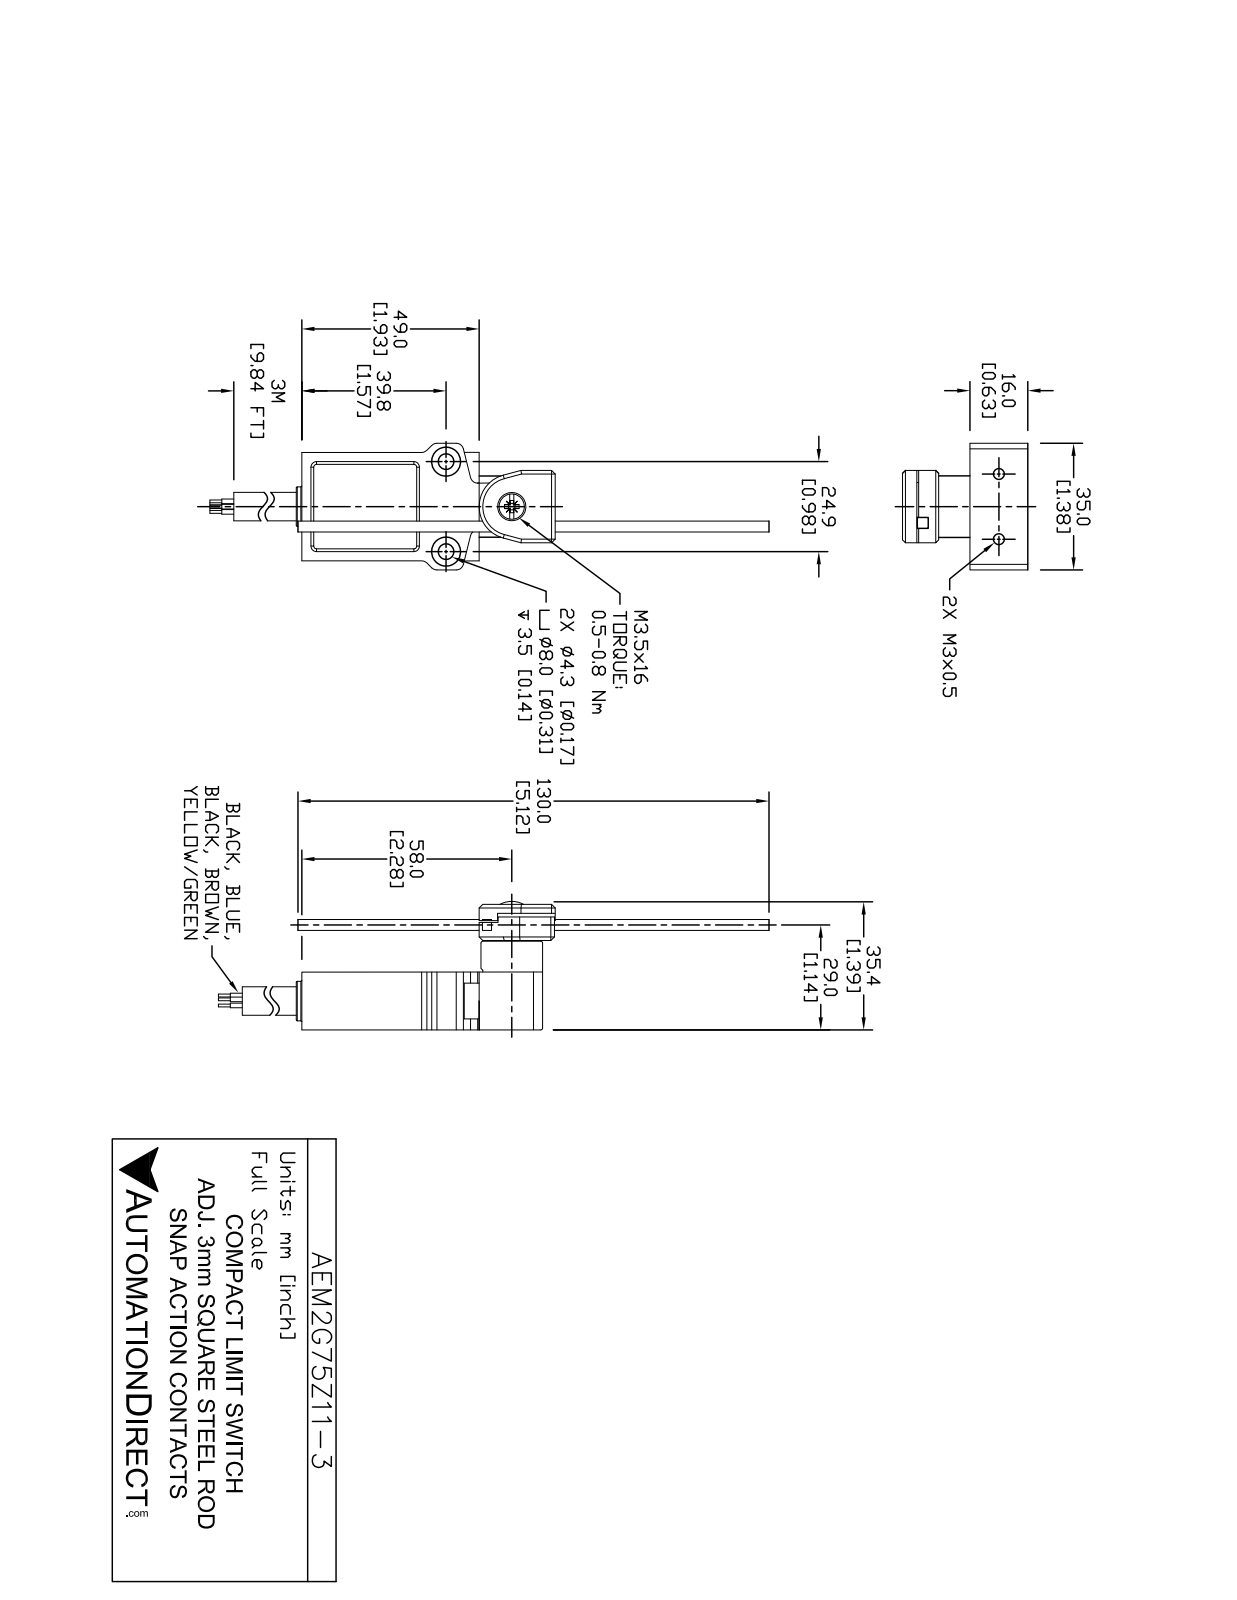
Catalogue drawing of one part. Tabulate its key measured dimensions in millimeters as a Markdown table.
| quantity | value |
| --- | --- |
| part name | AEM2G75Z11-3 |
| STEP written by | SolidWorks 2017 (AUTOMOTIVE_DESIGN) |
| units | millimeters |
| bodies | 7 solids, 223 faces (145 planar, 63 cylindrical, 15 other) |
| overall size | 174.1 × 47.5 × 34.7 |
| volume | 32 200 mm³ |
| surface area | 13 680 mm² |
| round holes (diameter × count) | 3 × 2, 4.4 × 2, 8.2 × 2, 3.5 × 1, 5 × 1, 8 × 1 |
| round bosses / shafts (diameter × count) | 15.8 × 1, 8.2 × 1, 7 × 1 |
| partial cylindrical surfaces (radius × count) | 2 × 8, 1.5 × 2, 4.4 × 1, 6.5 × 1, 6.6 × 1, 9 × 1 |
| main face-to-face distances | 16, 3, 27.9, 14.9, 30, 11.9, 30.9, 8, 22, 2.8 |
| hole center spacings | 21.9, 19, 25 |
